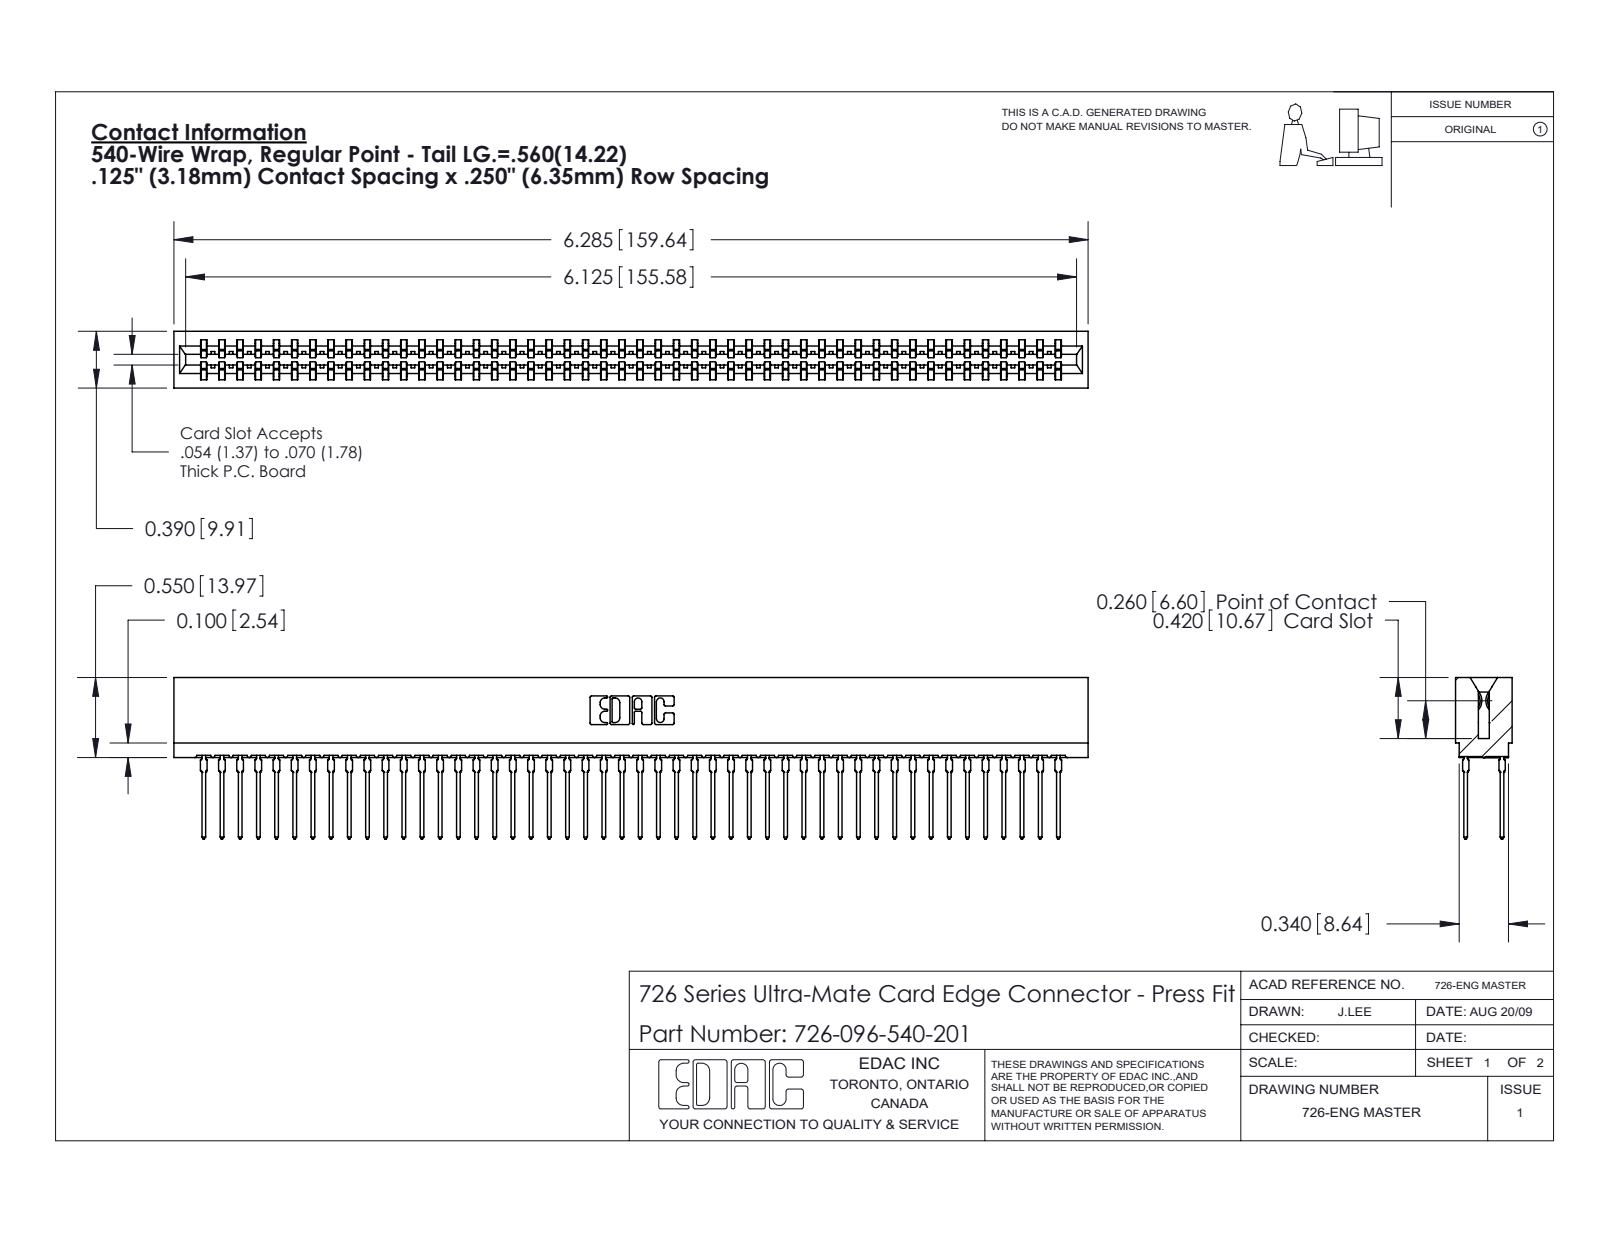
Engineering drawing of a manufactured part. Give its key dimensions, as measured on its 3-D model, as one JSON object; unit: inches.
{"part_name": "726 Part_.515 Slot Depth - 01; 726-096-540-201; 746-292-001_540", "step_written_by": "SolidWorks 2020 (CONFIG_CONTROL_DESIGN)", "units": "inches", "bodies": {"solids": 97, "faces": 8689, "planar": 4471, "cylindrical": 1722, "other": 2496}, "overall_size": [6.285, 1.109, 0.39], "volume_in3": 0.913, "surface_area_in2": 40.87, "partial_cylinders_radius": [[0.021, 192], [0.015, 49], [0.01, 22], [0.005, 8], [0.011, 8], [0.007, 6], [0.031, 6], [0.026, 3]], "face_to_face_distances": [0.057, 0.333, 0.025, 0.307, 0.39, 0.25, 0.083, 0.275, 0.365, 0.032]}
